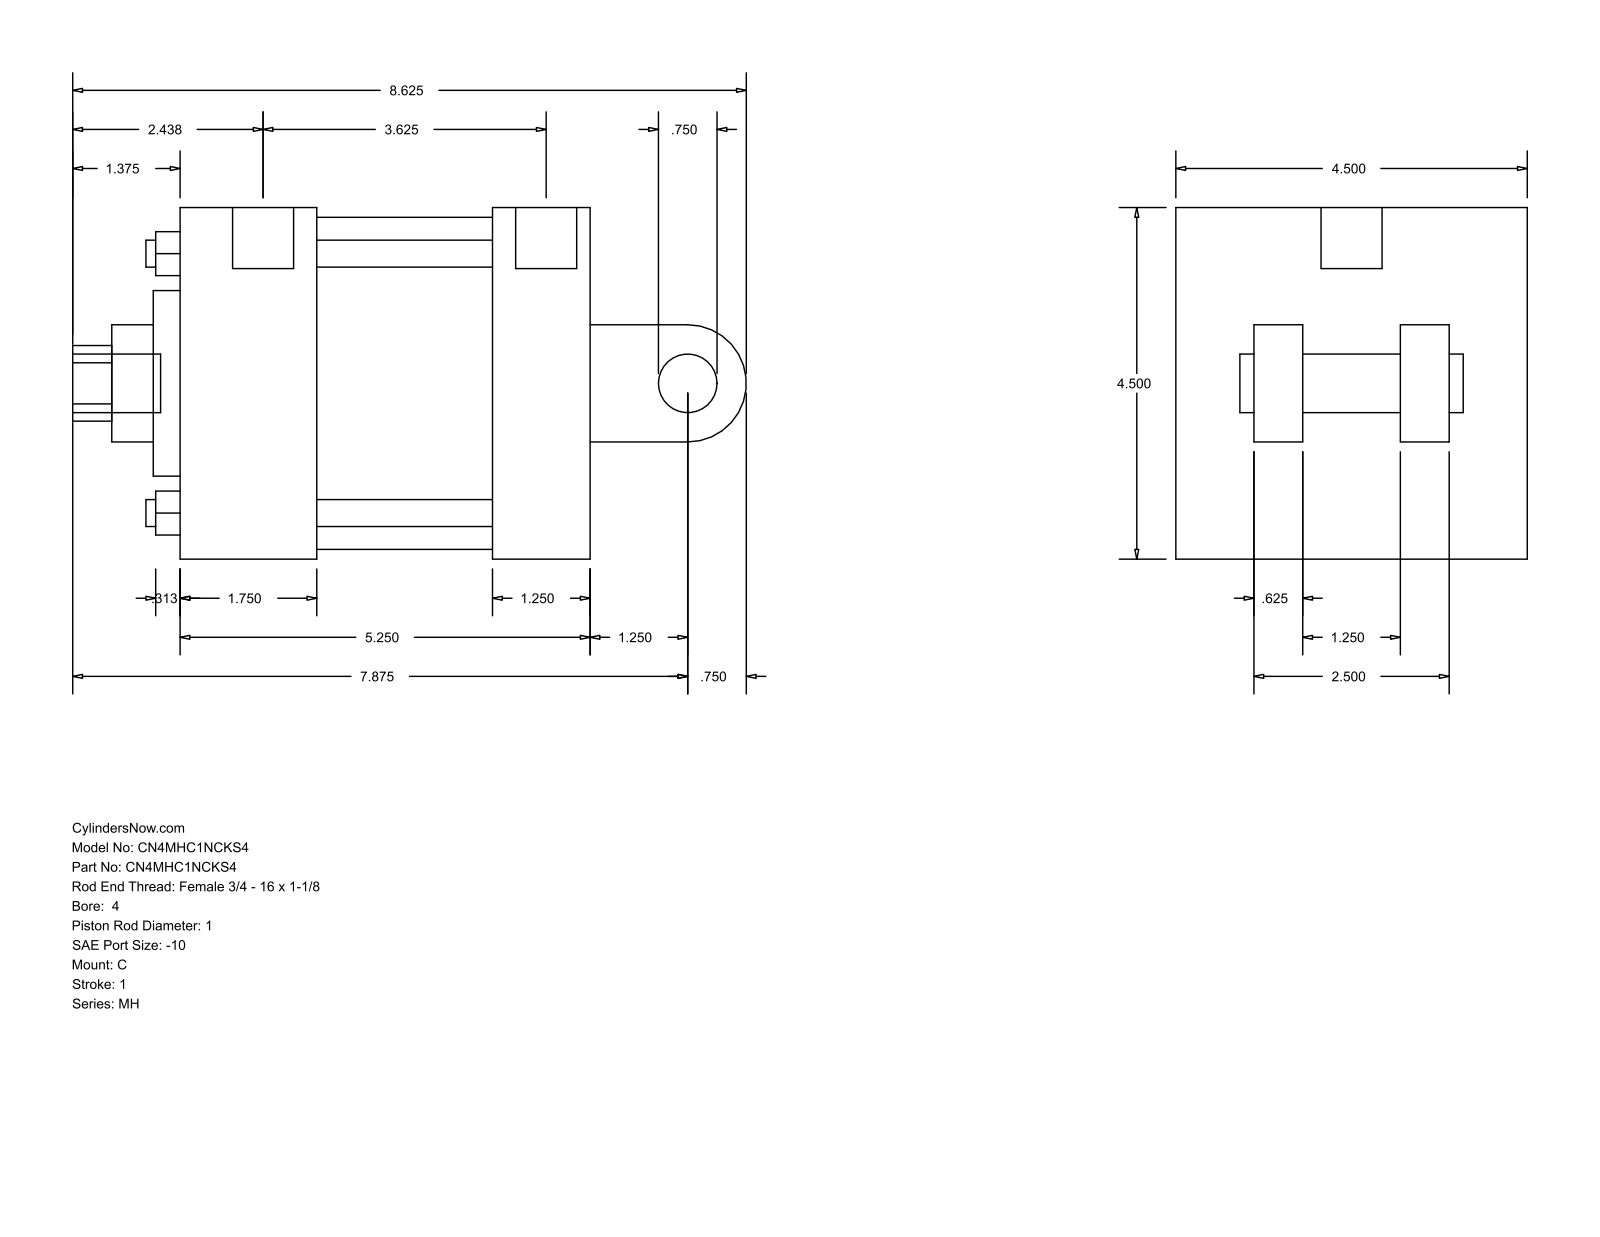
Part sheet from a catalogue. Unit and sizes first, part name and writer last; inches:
Units: inches
Overall size (bounding box): 8.625 × 4.5 × 4.5
Round holes (diameter × count): ⌀0.345 ×4, ⌀0.344 ×2, ⌀0.781 ×1, ⌀1 ×1, ⌀1.5 ×1, ⌀2.375 ×1, ⌀4.25 ×1
Round bosses / shafts (diameter × count): ⌀0.75 ×2, ⌀0.344 ×2, ⌀0.781 ×1
Partial cylindrical surfaces — rounded edges, fillets, slot ends (radius × count): R0.484 ×1, R0.75 ×1
Main face-to-face distances: 4.5, 5.25, 3.5, 1.75, 4, 2.25, 1.25, 2.875, 0.625, 1.875
Hole centre spacings: 2.347, 3.32, 4.695, 0.062
Bodies: 0 solids, 101 faces (71 planar, 30 cylindrical, 0 other)
Part name (STEP PRODUCT): MH_C__0400_1
STEP written by: GSSL Pune (CONFIG_CONTROL_DESIGN)
